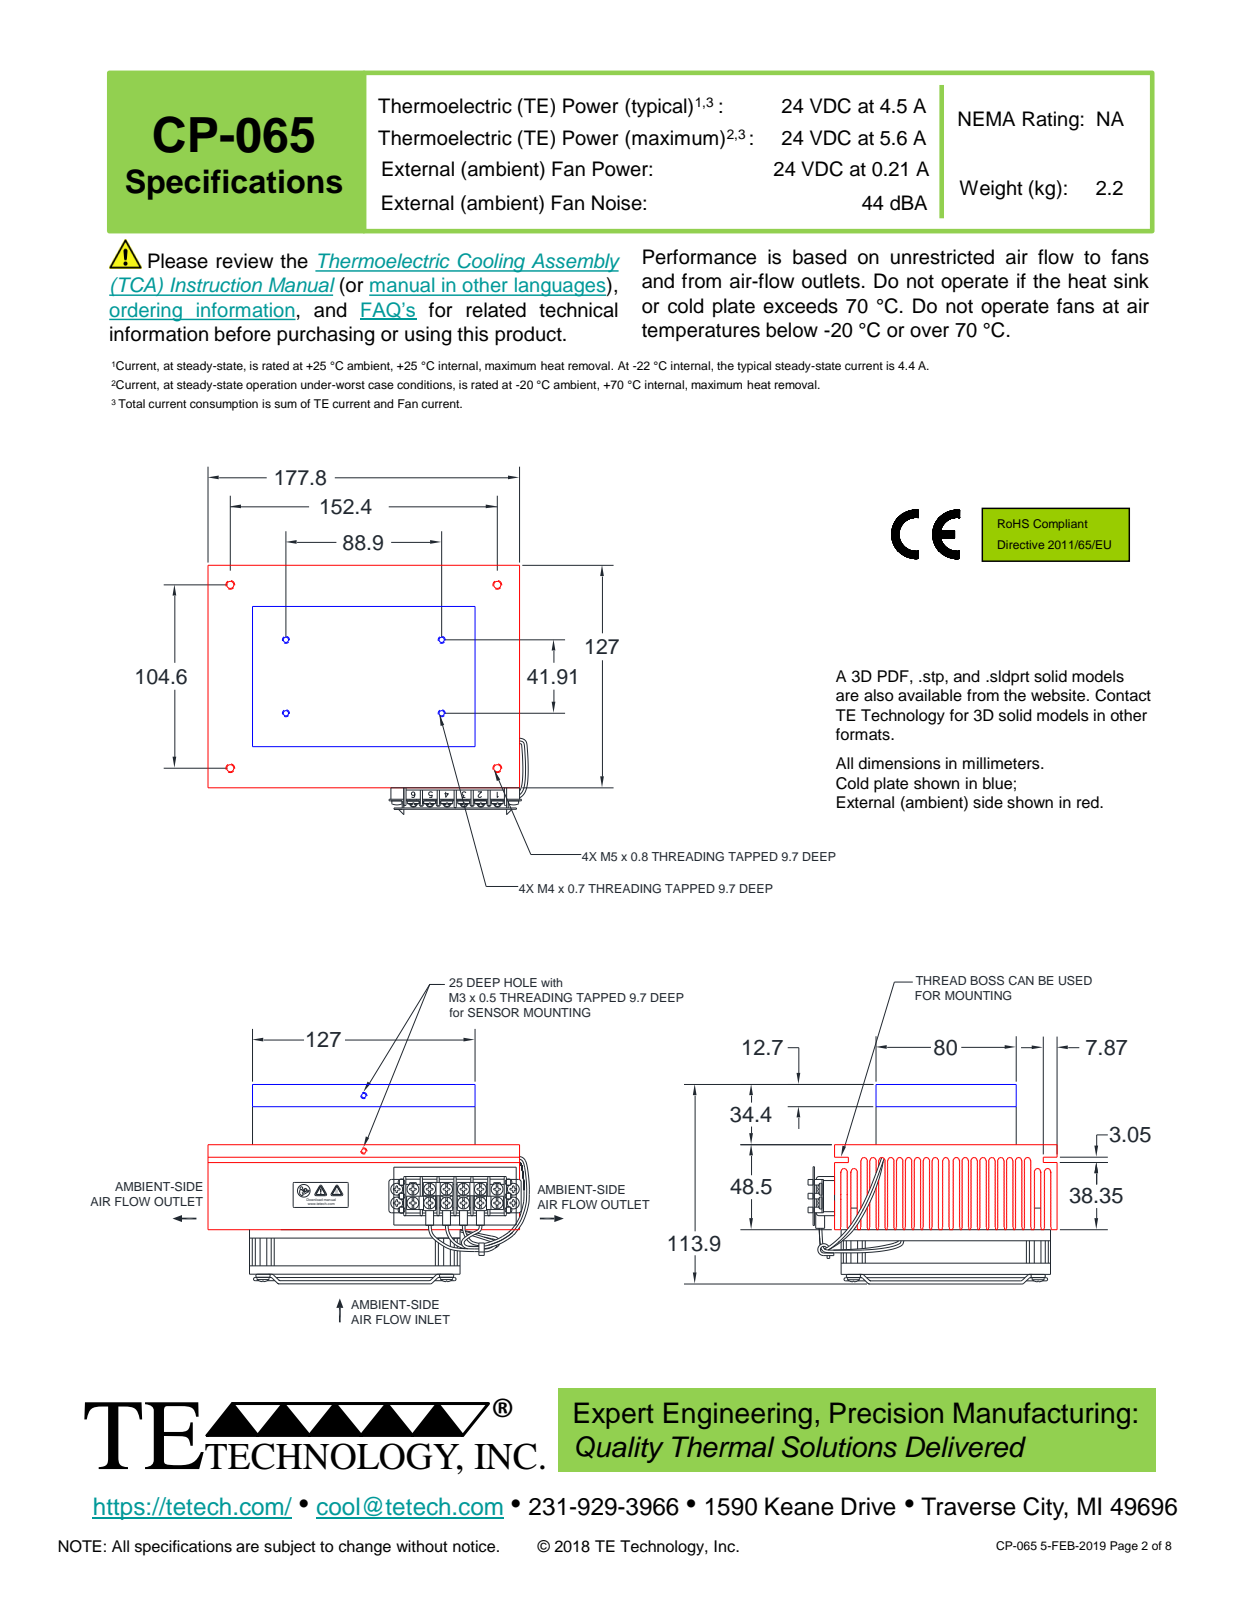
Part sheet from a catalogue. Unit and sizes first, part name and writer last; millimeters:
Units: millimetres
Overall size (bounding box): 178.6 × 142.2 × 113.9
Round holes (diameter × count): ⌀2.6 ×19, ⌀1.9 ×4, ⌀3.3 ×4, ⌀3.5 ×4, ⌀3.9 ×4, ⌀4.1 ×4, ⌀4.3 ×4, ⌀4.3 ×4, ⌀4.7 ×4, ⌀3 ×3, ⌀4.2 ×3, ⌀4.2 ×3
Round bosses / shafts (diameter × count): ⌀3.5 ×19, ⌀6.9 ×16, ⌀1.8 ×14, ⌀1.4 ×10, ⌀1.8 ×9, ⌀8.2 ×4, ⌀7.5 ×4, ⌀4.9 ×4
Partial cylindrical surfaces — rounded edges, fillets, slot ends (radius × count): R1 ×59, R0.8 ×54, R0.3 ×52, R1 ×21, R0.8 ×16, R2 ×15, R0.4 ×8, R0.8 ×8
Main face-to-face distances: 5.1, 10.2, 15.2, 52.7, 20.3, 57.8, 47.6, 25.4, 62.9, 42.5
Hole centre spacings: 19.1, 7.9, 20.6, 9.5, 9.5, 12.4, 74.1, 92.4
Volume: 993 400 mm³ · Surface area: 578 100 mm²
Bodies: 132 solids, 3537 faces (2094 planar, 669 cylindrical, 774 other)
Part name (STEP PRODUCT): 2660 CP-065 inner gasket; cover-clip; tb-600 terminal block; terminal-block-cover (+8 more)
STEP written by: Alibre (AUTOMOTIVE_DESIGN)
